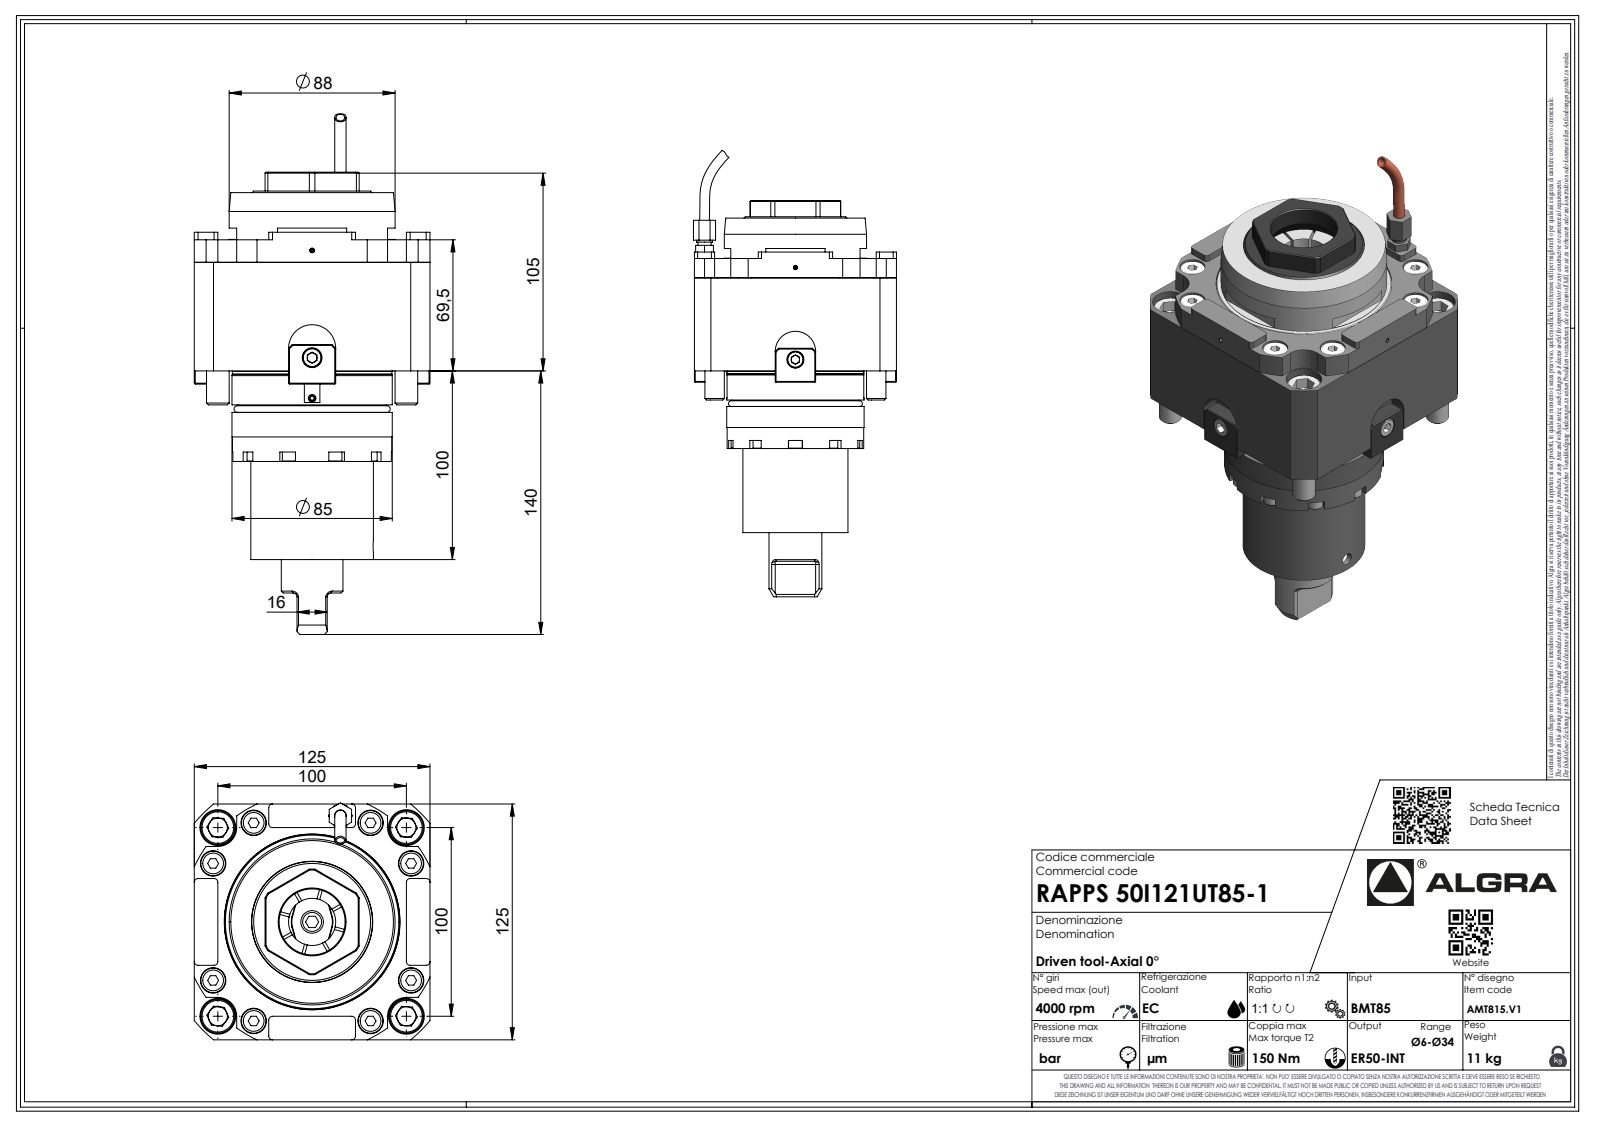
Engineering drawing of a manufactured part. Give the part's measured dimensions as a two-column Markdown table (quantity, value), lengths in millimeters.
| quantity | value |
| --- | --- |
| part name | RAPPS50I121UT85-1 |
| STEP written by | SolidWorks 2023 (AUTOMOTIVE_DESIGN) |
| units | millimeters |
| bodies | 1 solid, 592 faces (396 planar, 80 cylindrical, 116 other) |
| overall size | 275.99 × 125.59 × 125 |
| volume | 1 719 000 mm³ |
| surface area | 107 858 mm² |
| round holes (diameter × count) | 2.1 × 1 |
| round bosses / shafts (diameter × count) | 12 × 4, 88 × 1, 85 × 1, 65 × 1, 32.7 × 1, 9.8 × 1, 8.15 × 1, 6.37 × 1 |
| partial cylindrical surfaces (radius × count) | 2 × 22, 0.33 × 7, 0.52 × 7, 3.7 × 7, 10 × 4, 0.21 × 1, 28 × 1, 69 × 1 |
| main face-to-face distances | 125, 69.5, 48, 25, 100, 94.5, 169.5, 194.5, 52, 117.5 |
